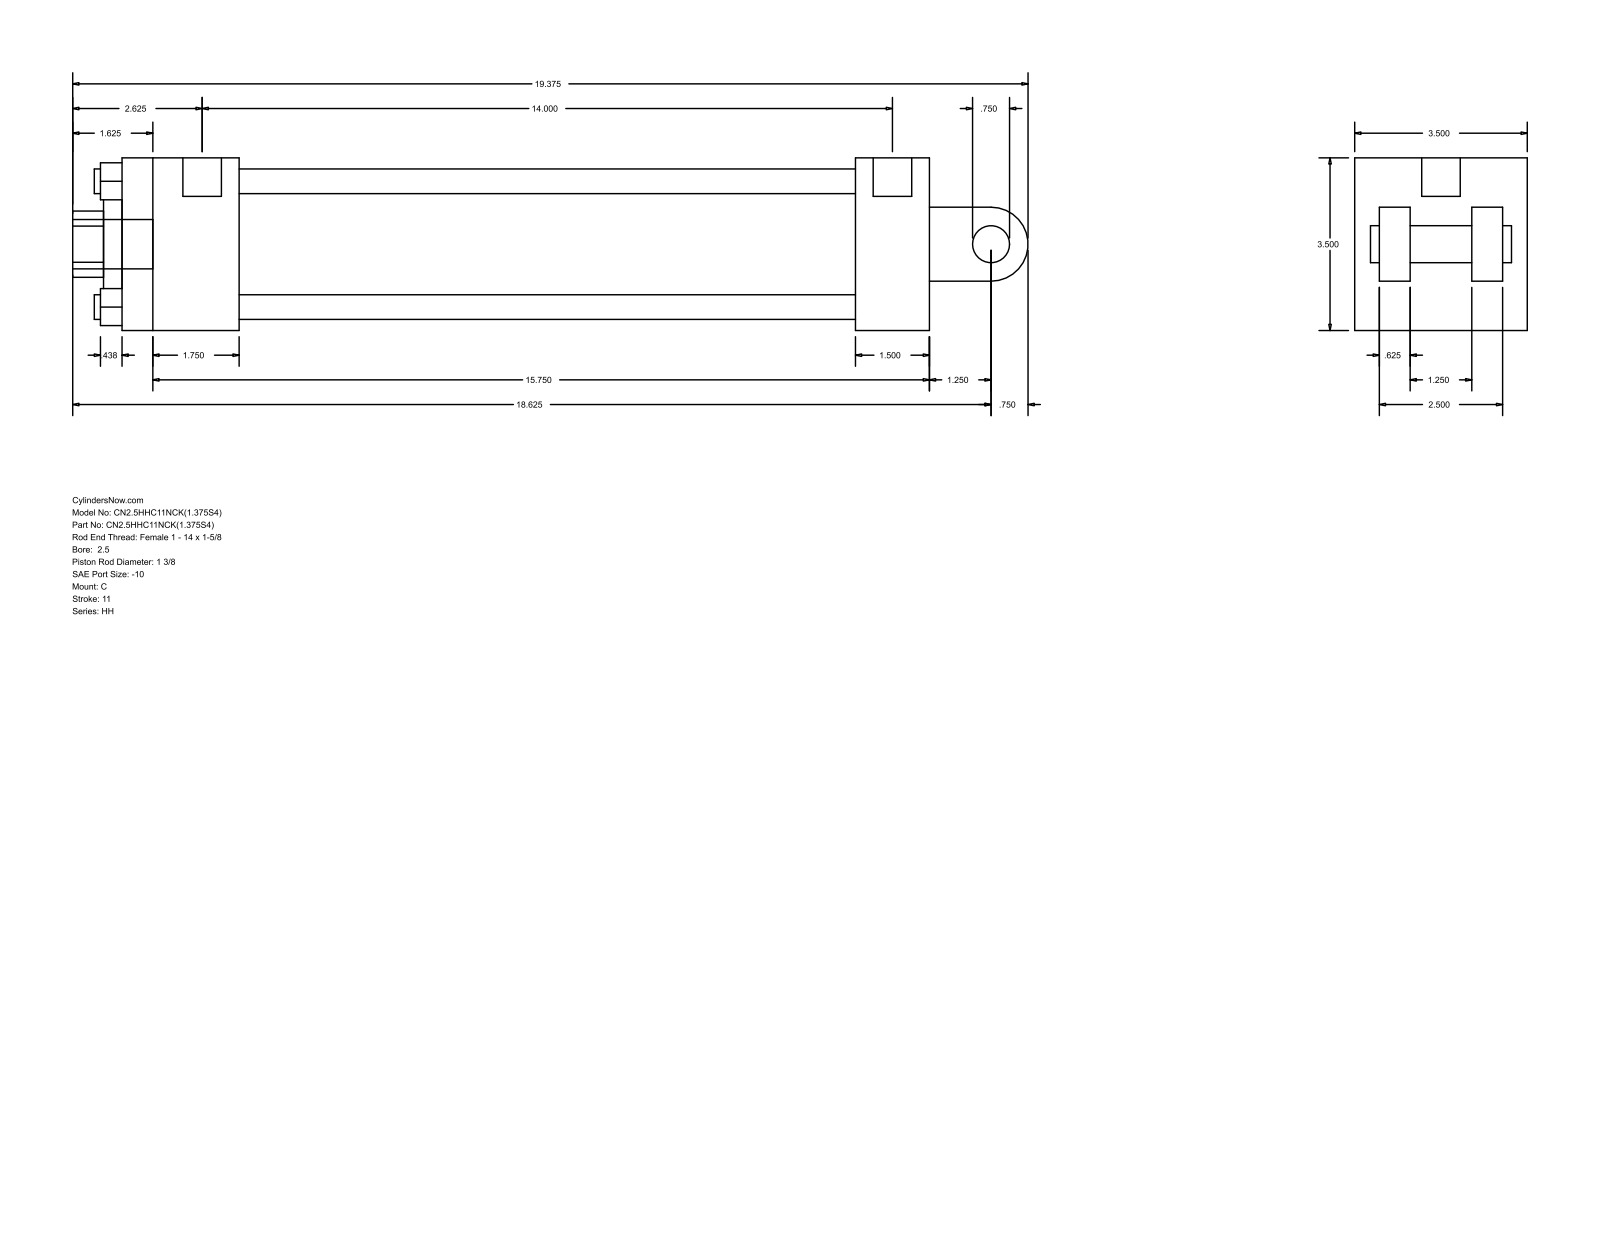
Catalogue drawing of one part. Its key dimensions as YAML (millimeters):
part_name: "HH_C__0250_1.375"
step_written_by: "GSSL Pune (CONFIG_CONTROL_DESIGN)"
units: millimeters
bodies: {solids: 0, faces: 99, planar: 70, cylindrical: 29, other: 0}
overall_size: [492.12, 88.9, 88.9]
round_holes:
  - {diameter: 12.7, count: 4}
  - {diameter: 5.56, count: 2}
  - {diameter: 19.84, count: 1}
  - {diameter: 34.92, count: 1}
  - {diameter: 50.8, count: 1}
  - {diameter: 73.03, count: 1}
round_bosses_or_shafts:
  - {diameter: 5.56, count: 2}
  - {diameter: 25.4, count: 1}
  - {diameter: 19.84, count: 1}
  - {diameter: 19.05, count: 1}
partial_cylinders:
  - {radius: 17.06, count: 1}
  - {radius: 19.05, count: 1}
face_to_face_distances: [88.9, 415.92, 63.5, 15.87, 12.7, 377.83, 38.09, 60.32, 317.51, 355.6]
hole_center_spacings: [45.79, 64.76, 91.58, 1.59]
